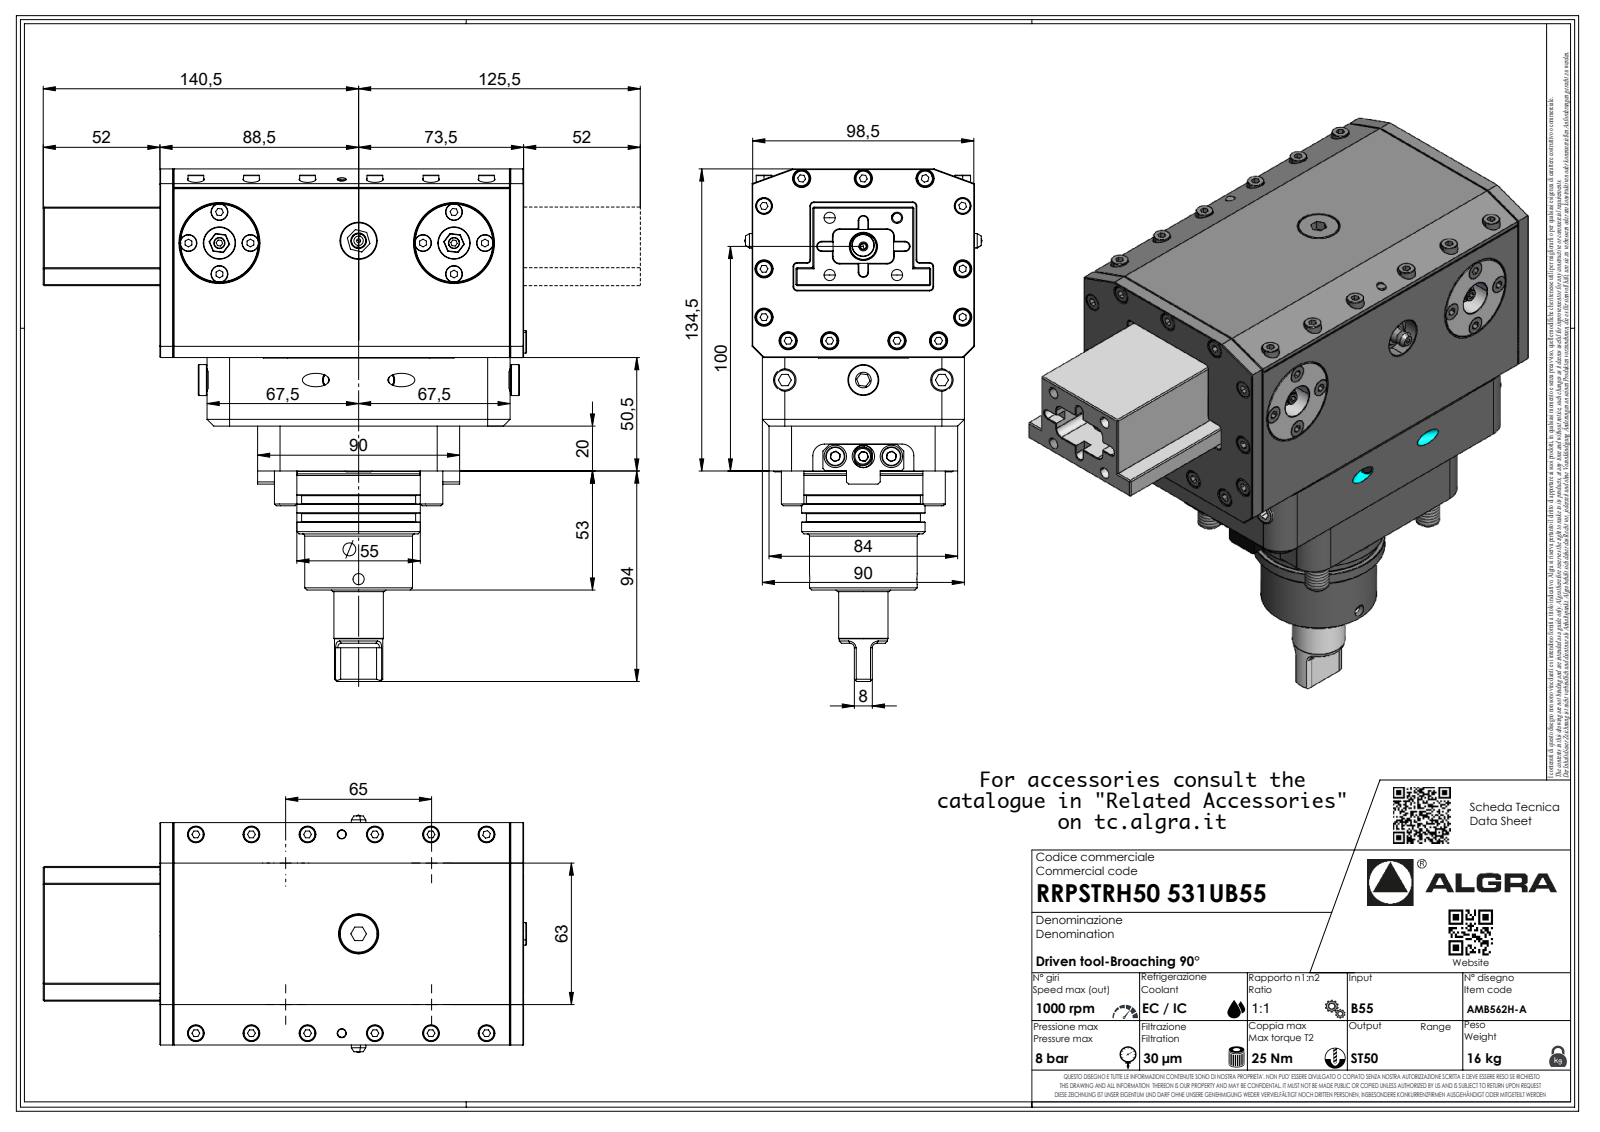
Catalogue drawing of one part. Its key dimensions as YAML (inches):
part_name: "RRPSTRH50531UB55"
step_written_by: "SolidWorks 2023 (AUTOMOTIVE_DESIGN)"
units: inches
bodies: {solids: 1, faces: 758, planar: 486, cylindrical: 86, other: 186}
overall_size: [8.984, 8.478, 4.157]
volume: 124.9
surface_area: 203.2
round_holes:
  - {diameter: 0.083, count: 1}
  - {diameter: 0.197, count: 1}
  - {diameter: 2.402, count: 1}
round_bosses_or_shafts:
  - {diameter: 0.276, count: 12}
  - {diameter: 2.165, count: 1}
  - {diameter: 2.15, count: 1}
  - {diameter: 2, count: 1}
  - {diameter: 1.89, count: 1}
  - {diameter: 0.866, count: 1}
  - {diameter: 0.846, count: 1}
  - {diameter: 0.394, count: 1}
partial_cylinders:
  - {radius: 0.394, count: 8}
  - {radius: 0.013, count: 7}
  - {radius: 0.02, count: 7}
  - {radius: 0.146, count: 7}
  - {radius: 0.079, count: 4}
  - {radius: 0.315, count: 4}
  - {radius: 0.207, count: 2}
  - {radius: 0.008, count: 1}
face_to_face_distances: [3.898, 3.307, 3.315, 0.177, 6.378, 3.72, 0.886, 2.047, 3.543, 1.98]
hole_center_spacings: [2.157]
